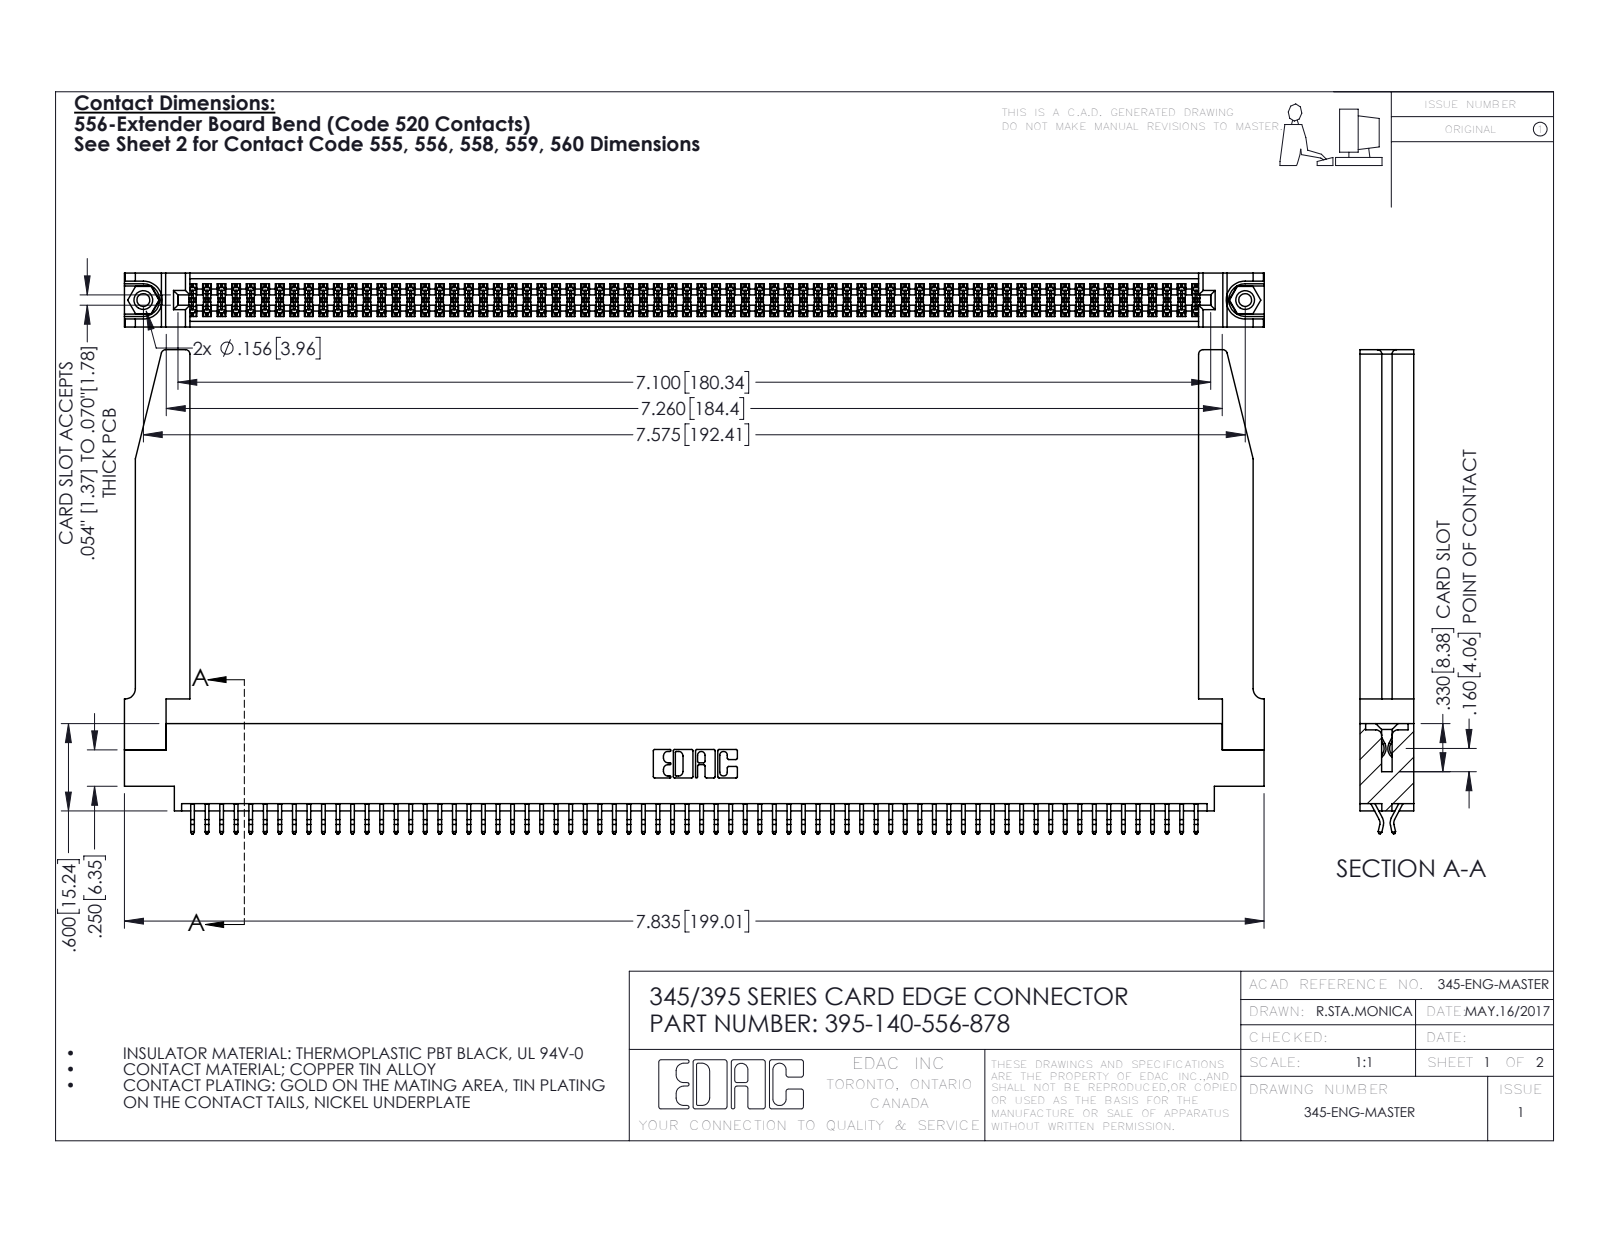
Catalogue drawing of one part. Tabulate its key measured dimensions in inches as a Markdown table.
| quantity | value |
| --- | --- |
| part name | 345 Part_0.170 Offset - 0.156 Dia-TH; 345-220-078_345-220-078; 345-250-001_345-250-001-102; 345-292-001_556 Tail (+1 more) |
| STEP written by | SolidWorks 2016 (CONFIG_CONTROL_DESIGN) |
| units | inches |
| bodies | 145 solids, 8204 faces (5406 planar, 2746 cylindrical, 52 other) |
| overall size | 7.836 × 3.327 × 0.37 |
| volume | 1.663 in³ |
| surface area | 56.09 in² |
| round holes (diameter × count) | 0.089 × 2, 0.125 × 2, 0.156 × 2, 0.064 × 1 |
| round bosses / shafts (diameter × count) | 0.155 × 2 |
| partial cylindrical surfaces (radius × count) | 0.006 × 210, 0.01 × 22, 0.03 × 8, 0.007 × 6, 0.031 × 6, 0.026 × 3, 0.01 × 2, 0.014 × 2 |
| main face-to-face distances | 0.072, 0.37, 0.298, 0.025, 0.098, 0.272, 0.2, 0.225, 0.175, 0.149 |
| hole center spacings | 0.27, 7.339, 7.575 |
